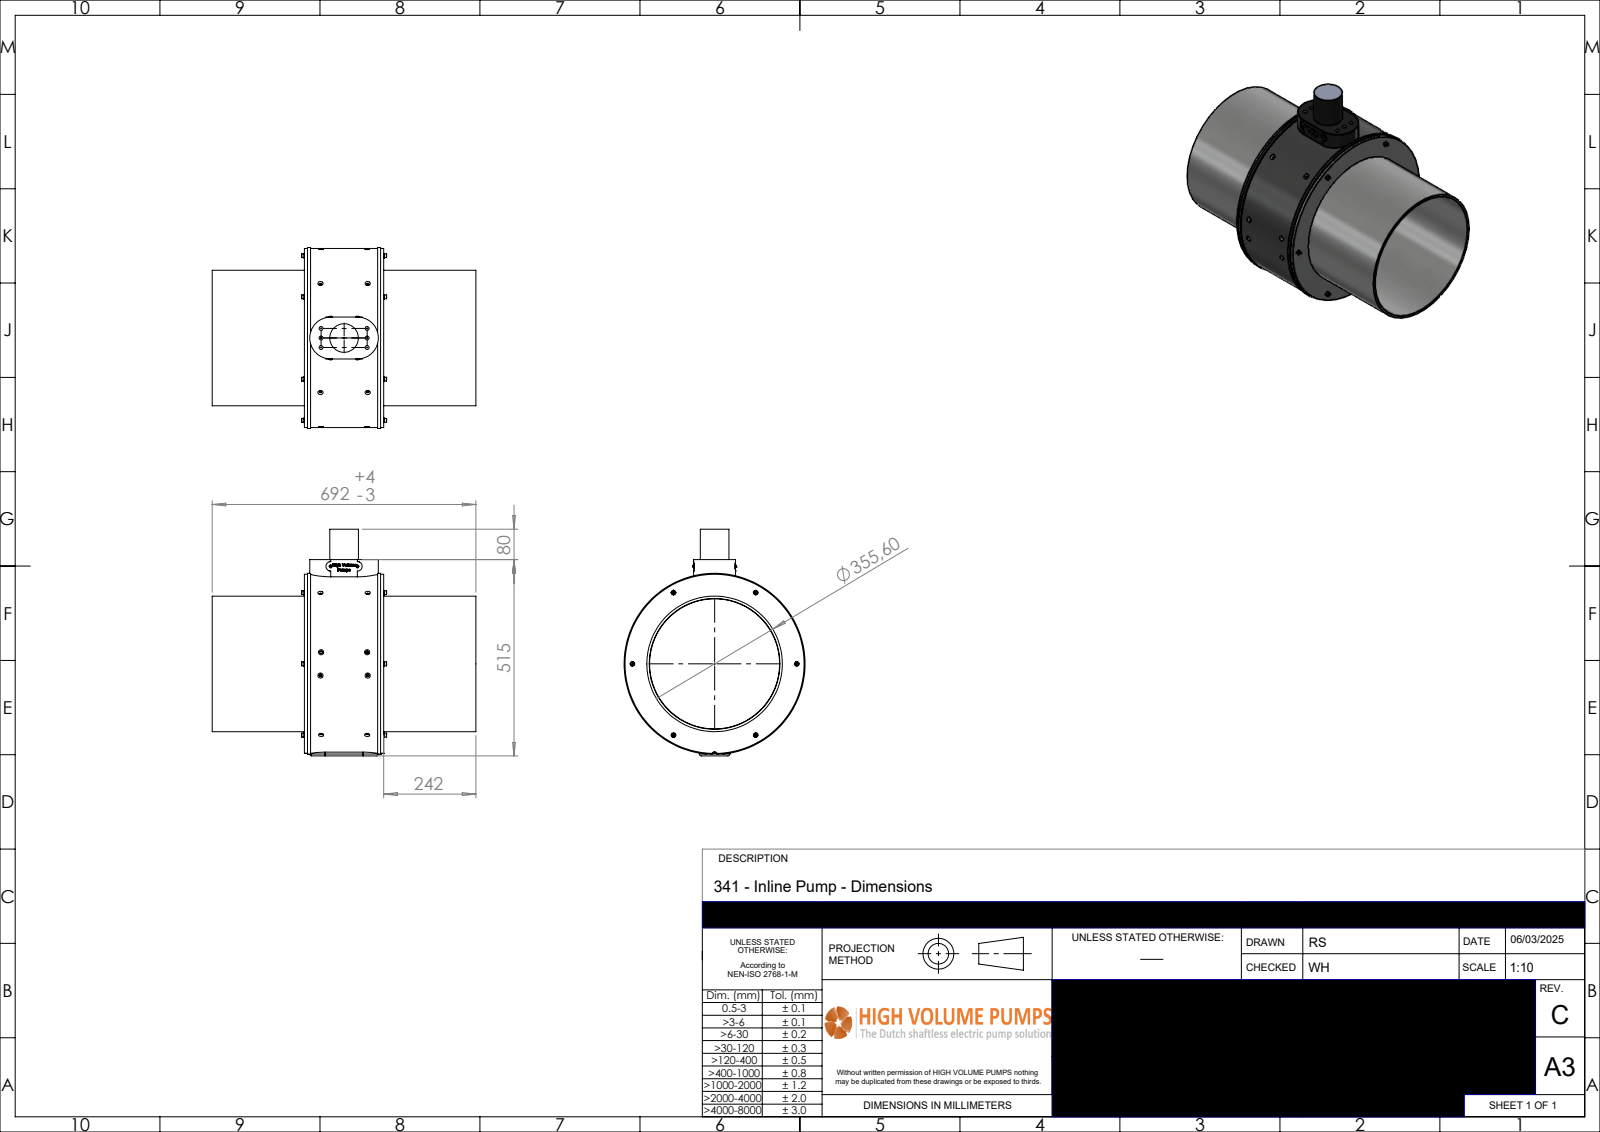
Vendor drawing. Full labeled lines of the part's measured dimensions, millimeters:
Part name (STEP PRODUCT): P-341-030-rev-C-IP
STEP written by: SolidWorks 2024 (AUTOMOTIVE_DESIGN)
Units: millimetres
Bodies: 1 solid, 1016 faces (573 planar, 127 cylindrical, 316 other)
Overall size (bounding box): 692 × 595.04 × 475
Volume: 21 620 000 mm³ · Surface area: 1 829 000 mm²
Round holes (diameter × count): ⌀6.6 ×22, ⌀5 ×16, ⌀10.2 ×6, ⌀341 ×1, ⌀343 ×1
Round bosses / shafts (diameter × count): ⌀12 ×6, ⌀11.57 ×6, ⌀10 ×6, ⌀7.6 ×2, ⌀475 ×1, ⌀470 ×1, ⌀355.6 ×1, ⌀75 ×1
Partial cylindrical surfaces — rounded edges, fillets, slot ends (radius × count): R5 ×8, R12.5 ×2, R40 ×2, R55 ×2, R178.5 ×1
Main face-to-face distances: 208, 8, 242, 450, 192, 515.04, 250, 442, 200, 258
Hole centre spacings: 122.5, 121, 1.52, 1.56, 25, 123.56, 124, 1.55
